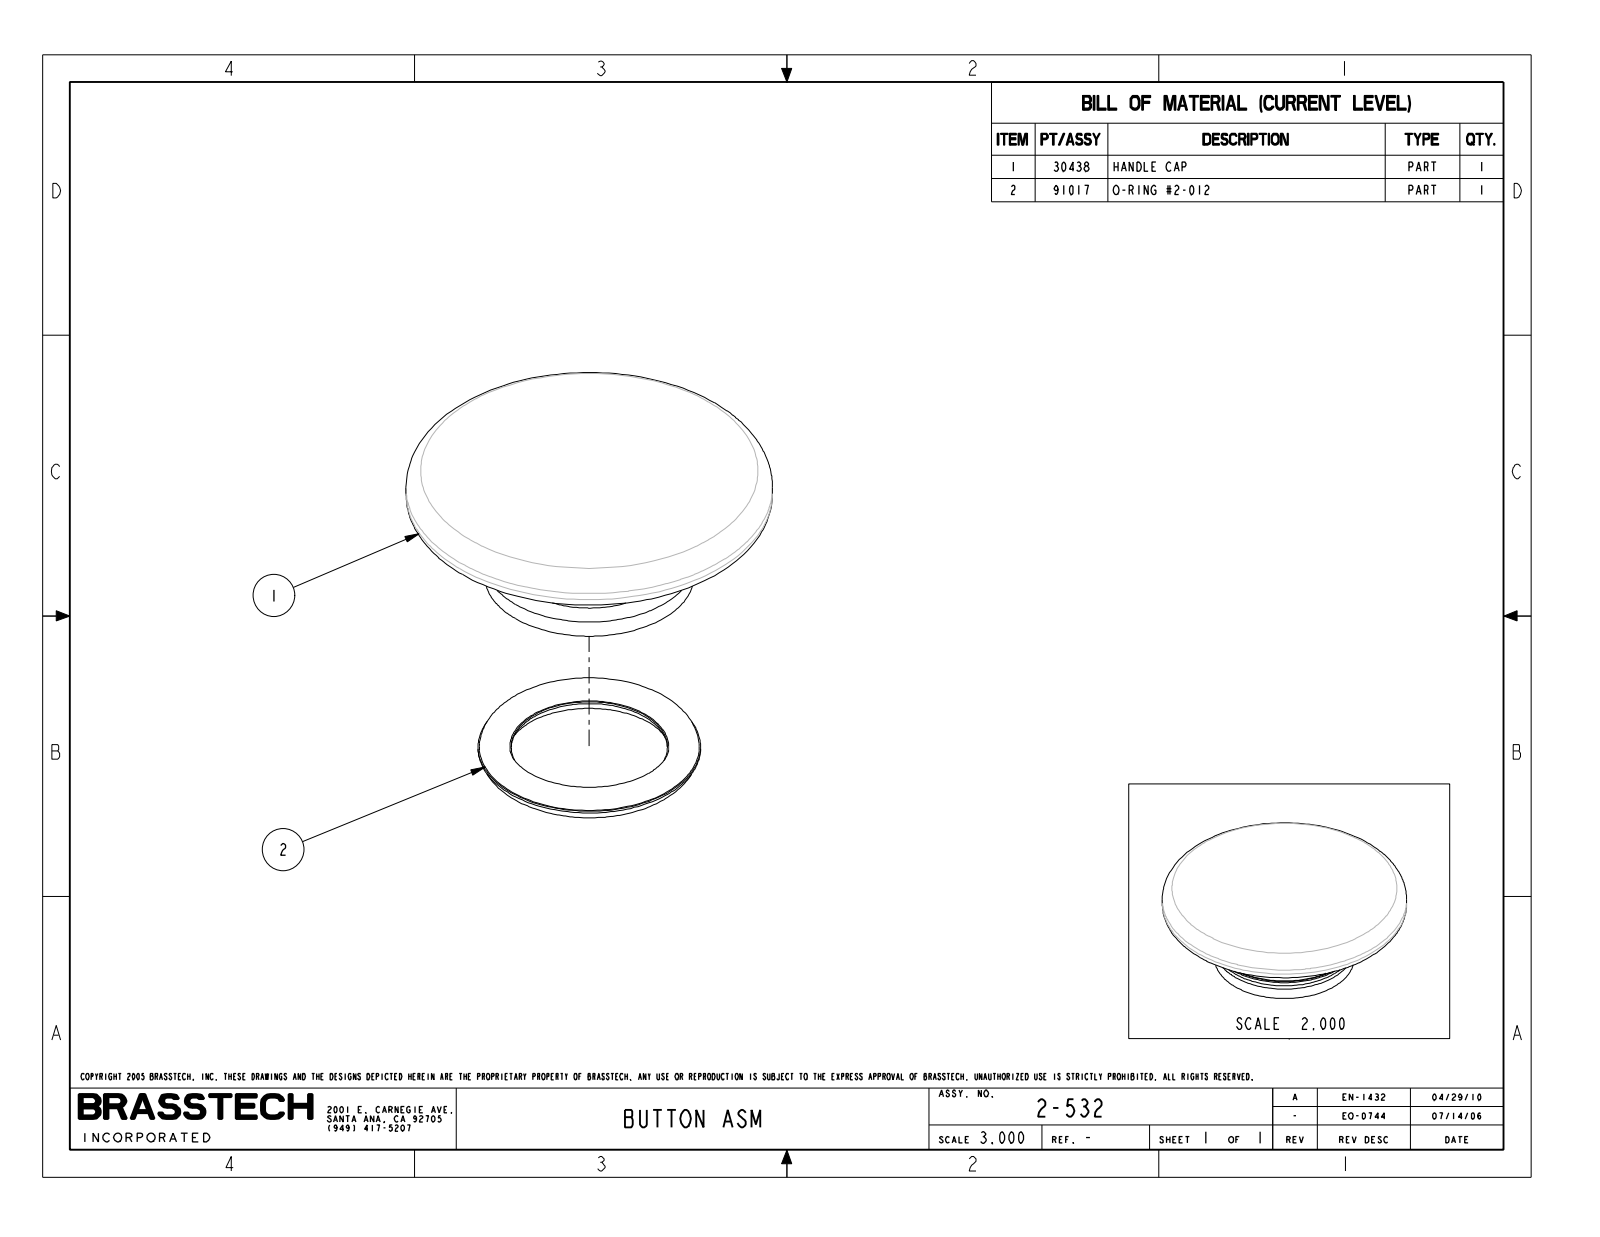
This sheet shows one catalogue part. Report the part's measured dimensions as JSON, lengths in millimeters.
{"part_name": "2-532_WEB", "step_written_by": "PRO/ENGINEER BY PARAMETRIC TECHNOLOGY CORPORATION, 2009300 (CONFIG_CONTROL_DESIGN)", "units": "millimeters", "bodies": {"solids": 1, "faces": 34, "planar": 6, "cylindrical": 16, "other": 12}, "overall_size": [21.3, 21.3, 9.1], "volume_mm3": 1400, "surface_area_mm2": 1404, "round_holes": [[1.6, 1], [7.1, 1]], "round_bosses_or_shafts": [[21.3, 1], [13, 1], [12.2, 1], [9.4, 1]], "face_to_face_distances": [2, 5.1, 3, 1, 4.1, 0.9, 1.1, 2.1, 3, 2]}
